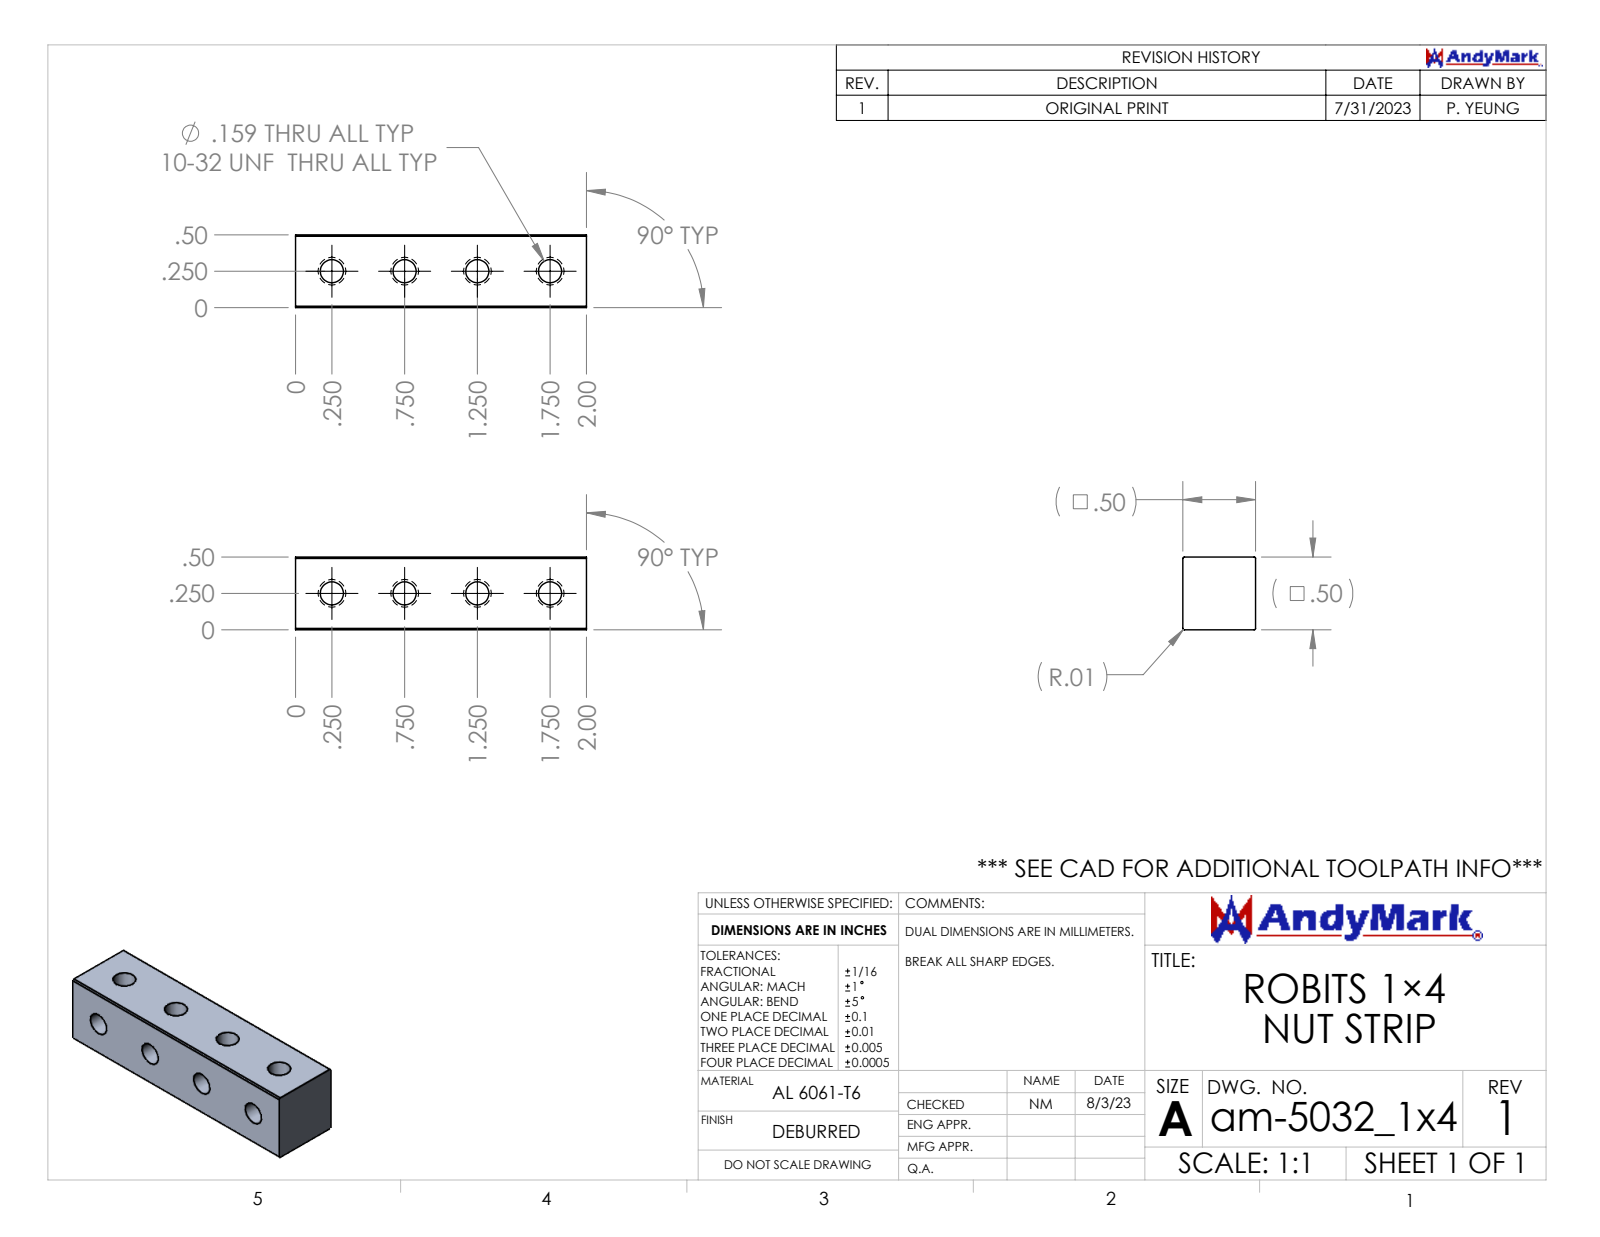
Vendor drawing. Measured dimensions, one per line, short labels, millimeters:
name: am-5032_1x4 Robits 1x4 Nut Strip
written by: SolidWorks 2022 (AUTOMOTIVE_DESIGN)
unit: mm
bodies: 1 solid, 42 faces (6 planar, 36 cylindrical, 0 other)
size: 50.8 × 12.7 × 12.7
volume: 7 060 mm³; area: 3 704 mm²
holes: 8× ⌀4
rounds: 4× R0.3
face distances: 12.7, 50.8
hole spacings: 12.7, 25.4, 38.1
